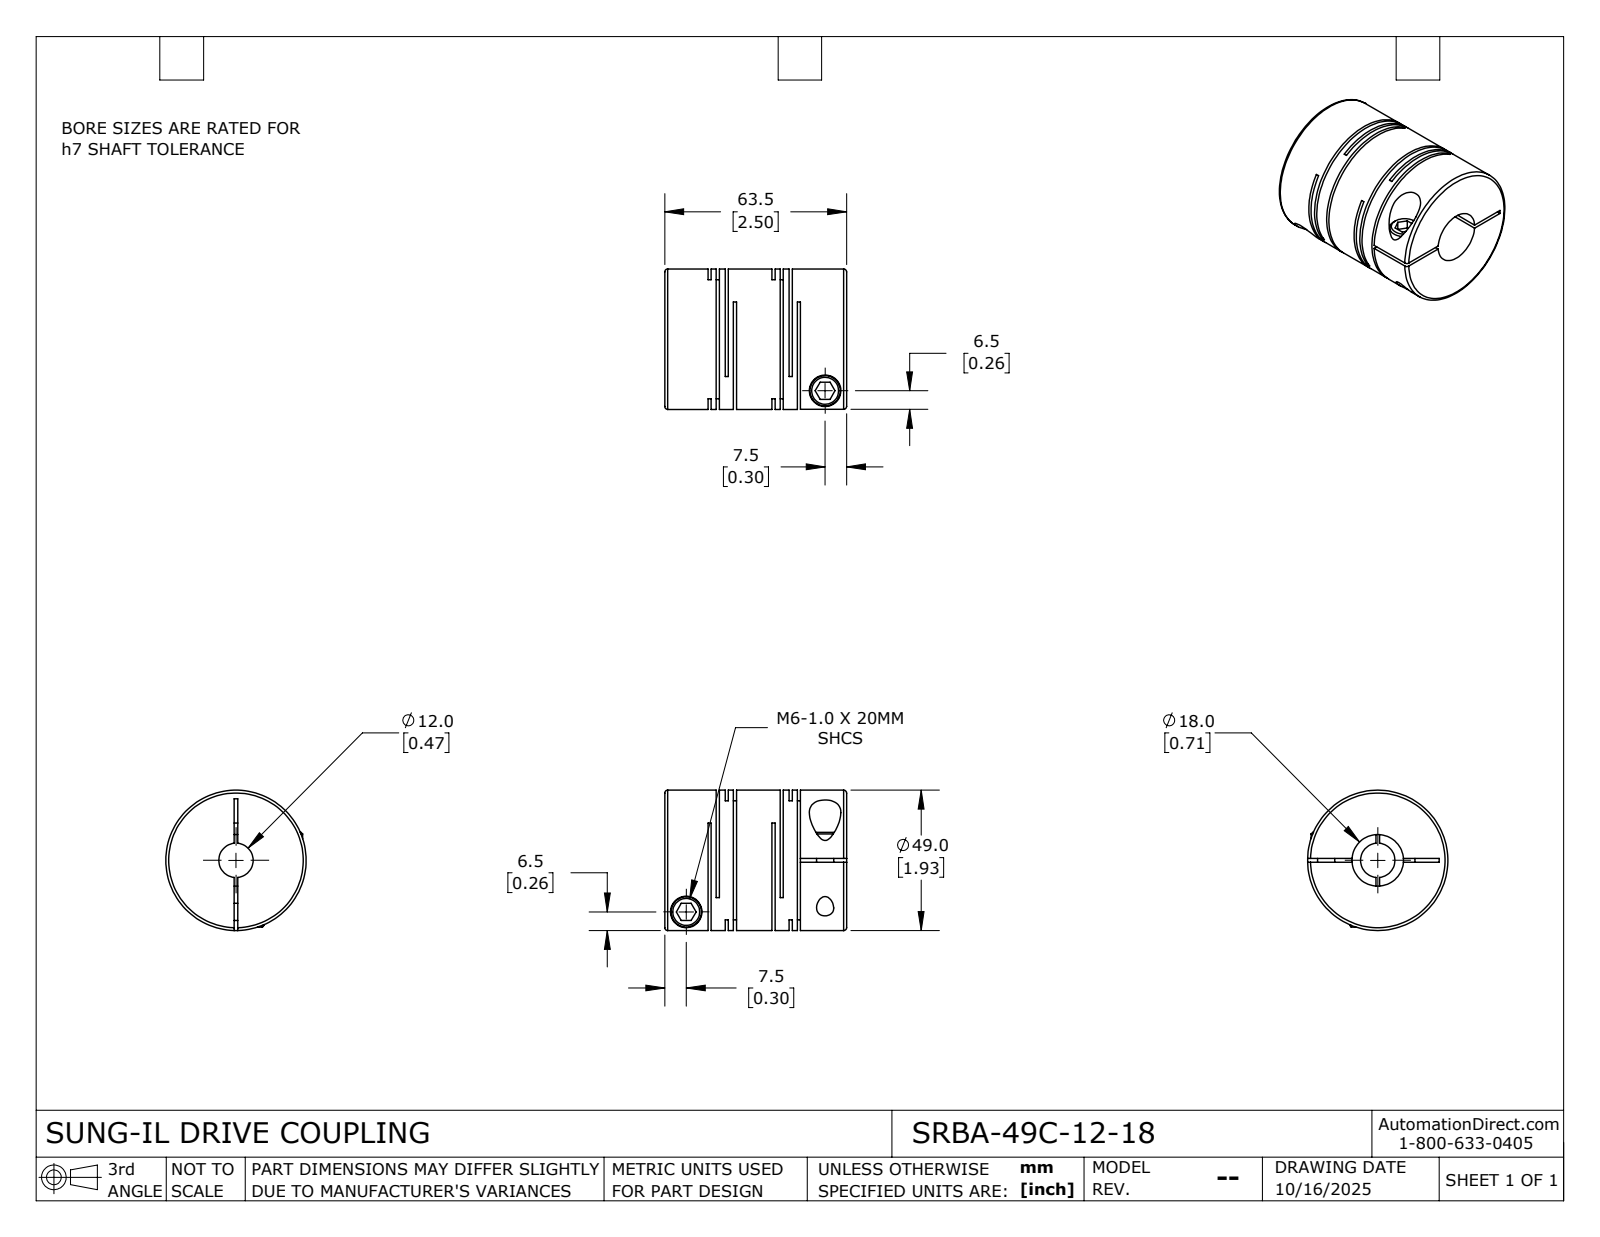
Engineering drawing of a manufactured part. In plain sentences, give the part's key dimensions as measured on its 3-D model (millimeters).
The part is named "SRBA-49C-12-18". Its 3-D file was written by "SolidWorks 2024 (CONFIG_CONTROL_DESIGN)". It is 1 solid with 115 faces: 60 planar, 42 cylindrical and 13 other. Overall it measures 63.5 by 49 by 49 millimeters. Its volume is 91 410 cubic millimeters and its surface area 38 985 square millimeters. Round holes: 2 of diameter 6, 2 of diameter 11, 1 of diameter 12, 1 of diameter 18. Round bosses or shafts: 2 of diameter 10.6, 1 of diameter 49. The main face-to-face distances are 6, 1.1, 22.35, 2.85, 21.25, 3.15, 19.5, 16.35, 1.75, 4.9.
